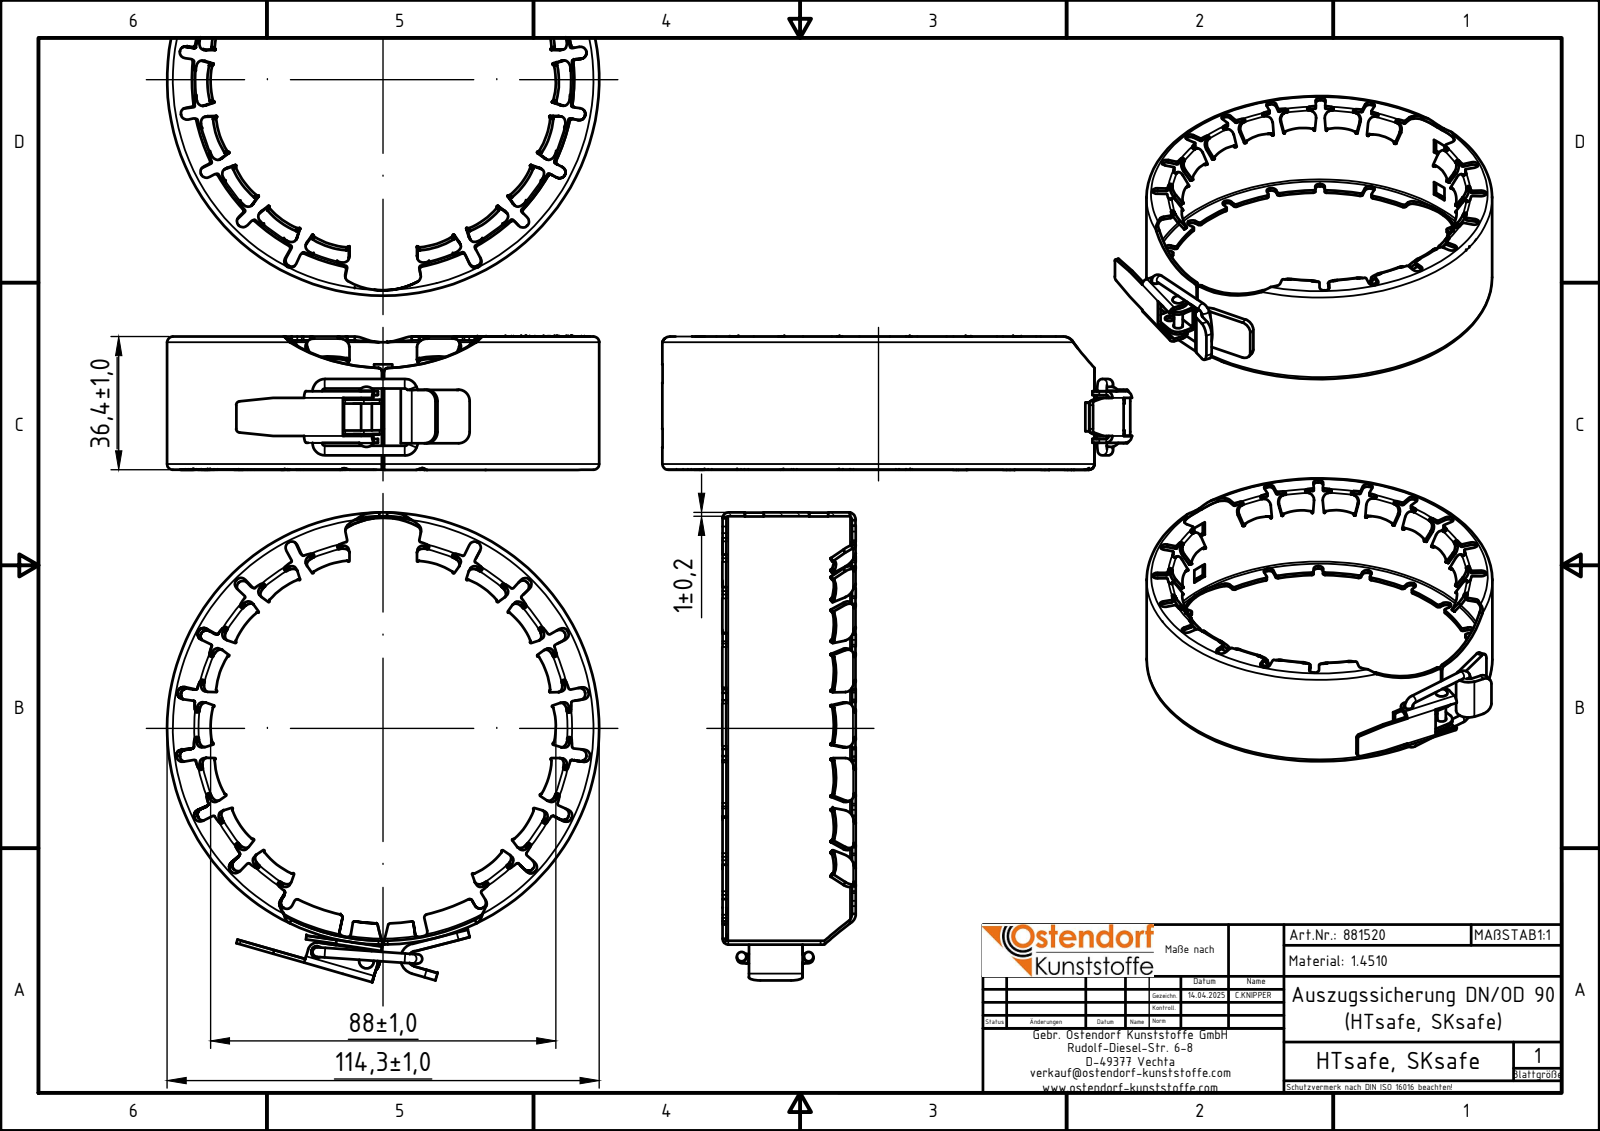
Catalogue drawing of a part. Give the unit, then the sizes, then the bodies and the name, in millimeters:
Units: millimetres
Overall size (bounding box): 122.92 × 113.06 × 34.87
Round holes (diameter × count): ⌀3 ×3
Round bosses / shafts (diameter × count): ⌀2.5 ×3, ⌀2.8 ×1
Partial cylindrical surfaces — rounded edges, fillets, slot ends (radius × count): R2.95 ×7, R3 ×5, R1 ×4, R2.96 ×3, R0.74 ×2, R1.74 ×2, R2.95 ×2, R2.96 ×2
Main face-to-face distances: 1, 2, 12.48, 8, 2.23, 10.25, 10.23, 2.25, 13.48, 11.48
Hole centre spacings: 5.01, 8.05, 13.06
Volume: 17 683 mm³ · Surface area: 36 166 mm²
Bodies: 6 solids, 1089 faces (136 planar, 51 cylindrical, 902 other)
Part name (STEP PRODUCT): 881520z
STEP written by: Autodesk Inventor 2024 (AUTOMOTIVE_DESIGN)
